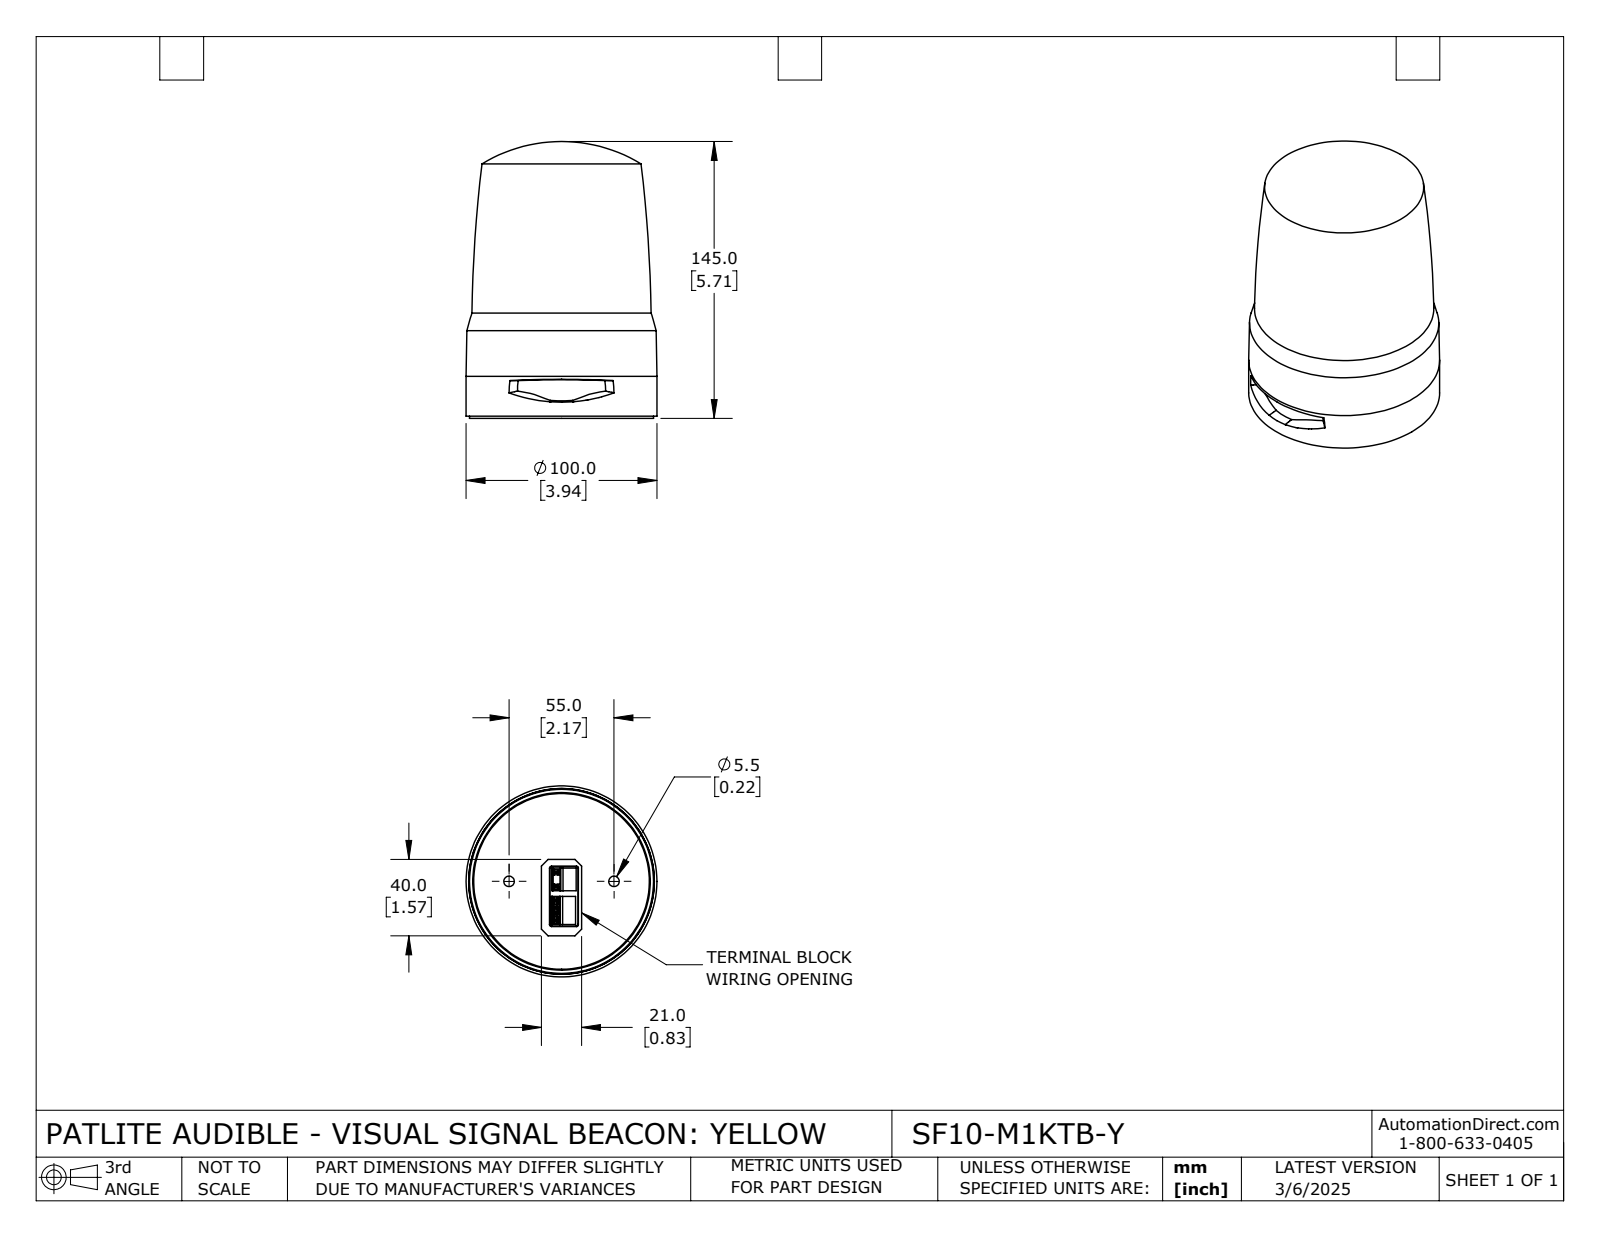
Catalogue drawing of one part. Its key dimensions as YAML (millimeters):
part_name: "SF10-M1KTB-Y"
step_written_by: "SolidWorks 2024 (CONFIG_CONTROL_DESIGN)"
units: millimeters
bodies: {solids: 2, faces: 275, planar: 174, cylindrical: 31, other: 70}
overall_size: [145, 100, 100]
volume: 875277
surface_area: 79857
round_holes:
  - {diameter: 5.5, count: 2}
  - {diameter: 13, count: 2}
  - {diameter: 93, count: 1}
round_bosses_or_shafts:
  - {diameter: 100, count: 1}
  - {diameter: 96.4, count: 1}
  - {diameter: 94.5, count: 1}
  - {diameter: 93.2, count: 1}
  - {diameter: 92, count: 1}
partial_cylinders:
  - {radius: 1, count: 4}
  - {radius: 0.3, count: 2}
  - {radius: 44.75, count: 1}
  - {radius: 45, count: 1}
face_to_face_distances: [6.3, 18.2, 11.9, 5.6, 12.6, 5.1, 0.4, 4.7, 1.2, 17]
hole_center_spacings: [27.5, 55]
